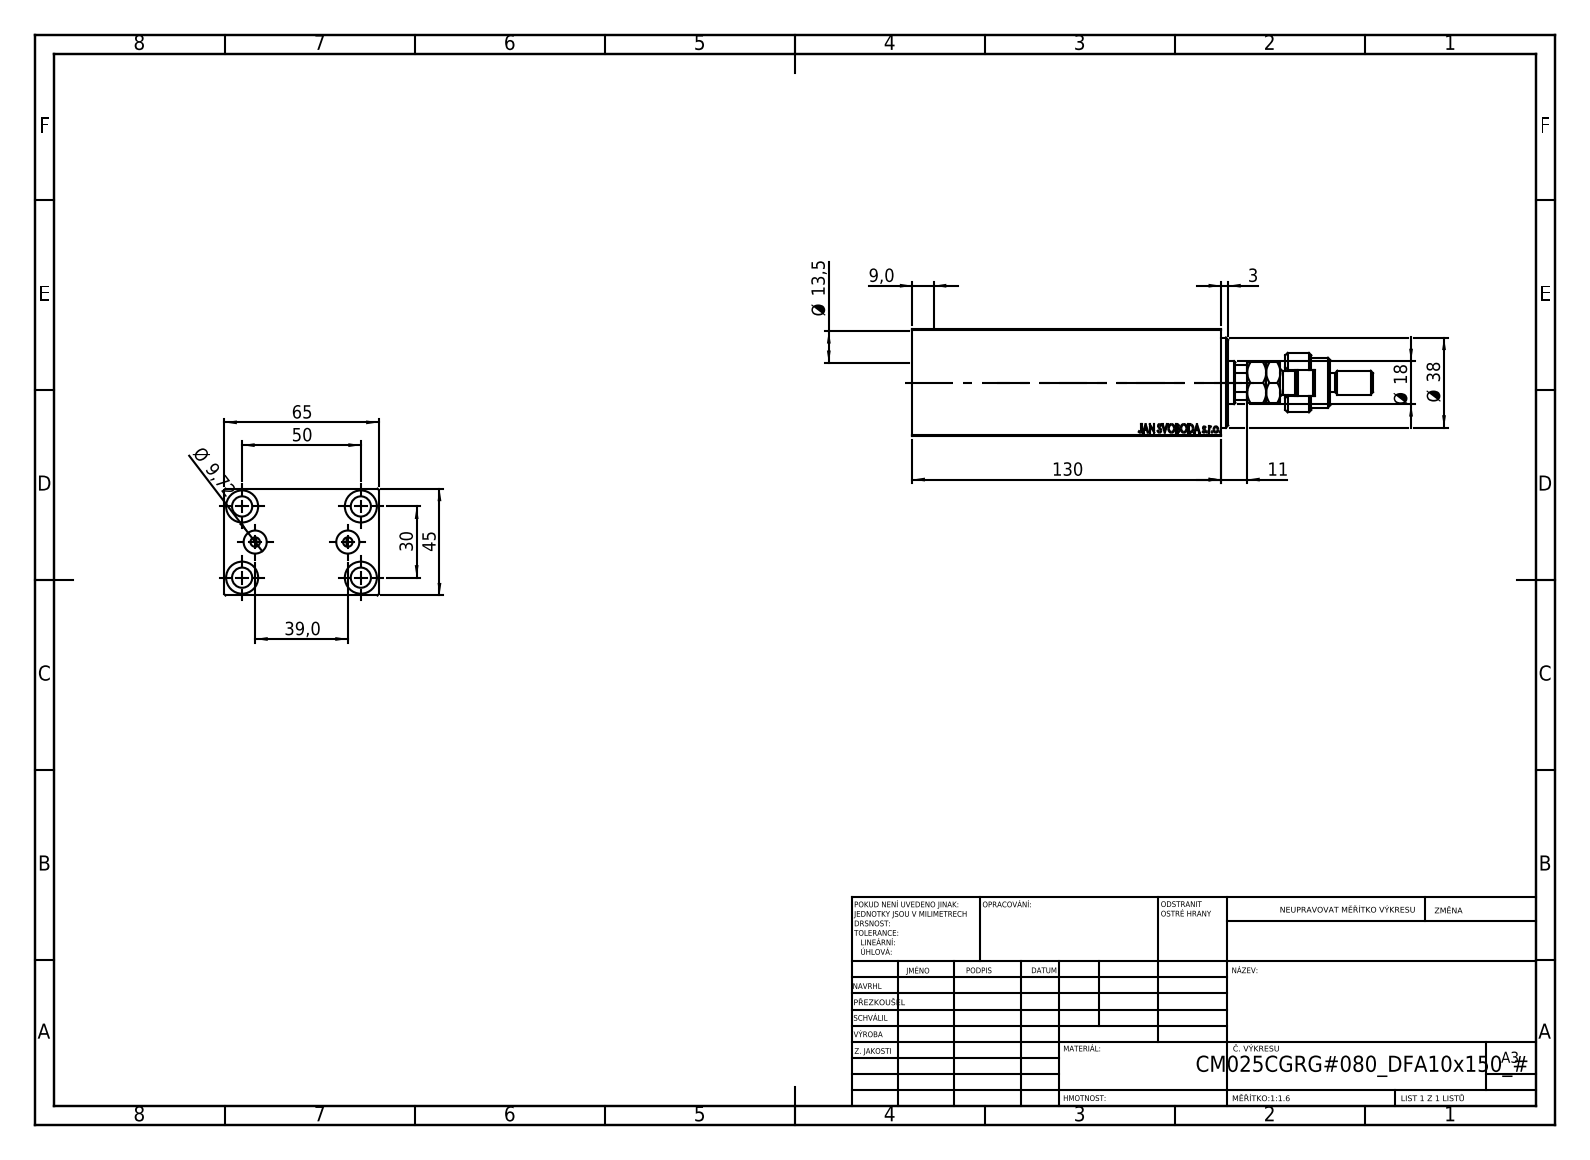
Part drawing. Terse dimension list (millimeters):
name: V450CM_C_Body; MFA; FEMALE_PART_FOR_DFA; V450CM_VC_B (+1 more)
written by: SolidWorks 2019 (CONFIG_CONTROL_DESIGN)
unit: mm
bodies: 5 solids, 943 faces (436 planar, 69 cylindrical, 438 other)
size: 194 × 65 × 45
volume: 336 945 mm³; area: 81 516 mm²
holes: 5× ⌀8.5, 4× ⌀13.5, 2× ⌀4, 2× ⌀9.72, 1× ⌀18, 1× ⌀21.5, 1× ⌀27, 1× ⌀38
bosses: 1× ⌀25, 1× ⌀21, 1× ⌀16, 1× ⌀10, 1× ⌀8
rounds: 1× R5.5, 1× R8.5, 1× R8.75
face distances: 45, 65, 6, 119, 124, 130, 5, 14, 3, 125
hole spacings: 15.98, 29.15, 46.96, 19.5, 30, 50, 58.31, 39
